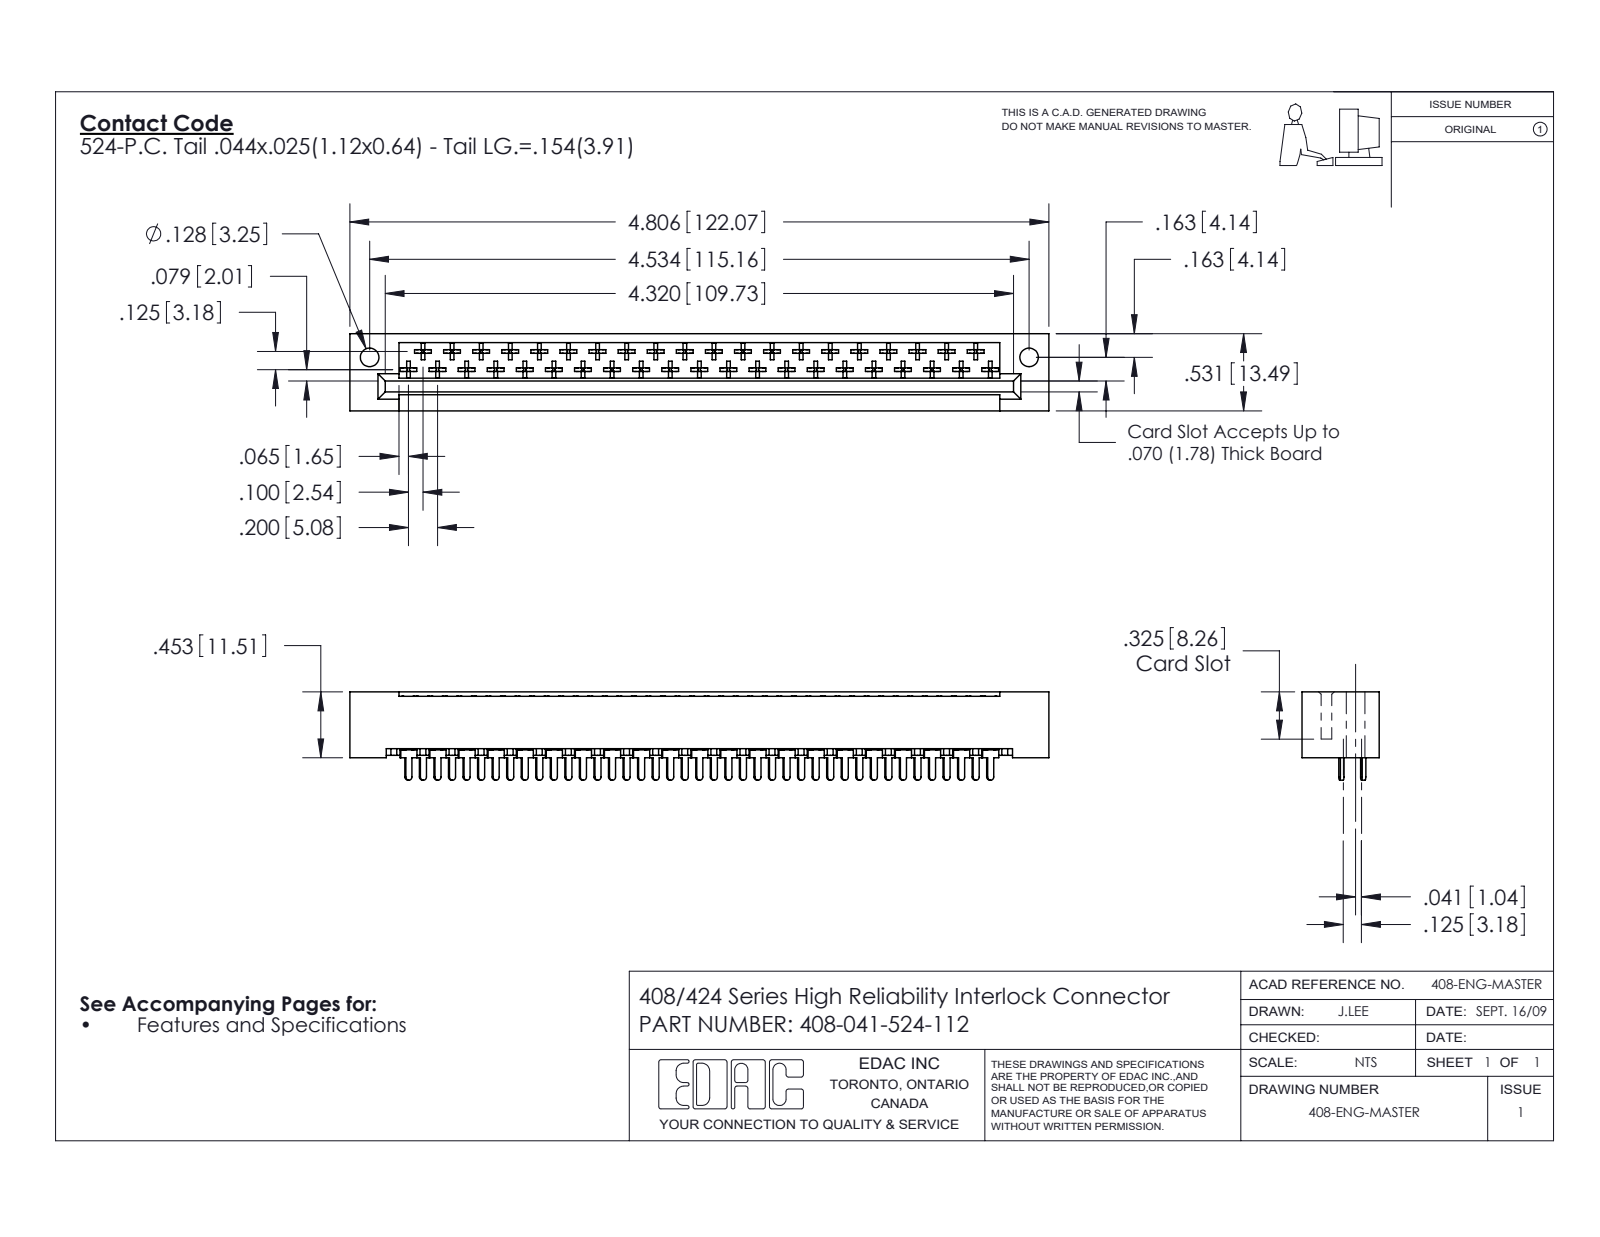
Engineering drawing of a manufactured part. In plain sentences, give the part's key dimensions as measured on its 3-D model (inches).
The part is named "408-041-524-112; 408 Part_041 - 1; 408-290-001_408-290-124 - Bottom; 408-290-001_408-290-124 - Top". Its 3-D file was written by "SolidWorks 2016 (CONFIG_CONTROL_DESIGN)". It is 42 solids with 2299 faces: 1758 planar, 377 cylindrical and 164 other. Overall it measures 4.806 by 0.607 by 0.531 inches. Its volume is 0.85 cubic inches and its surface area 25.92 square inches. Round holes: 2 of diameter 0.128. Partial cylindrical surfaces (rounded edges, fillets, slot ends): 246 of radius 0.01, 43 of radius 0.02, 41 of radius 0.022. The main face-to-face distances are 0.531, 0.125, 0.1, 0.025, 0.025, 0.4, 0.259, 0.272, 0.235, 0.296. The hole center spacings are 4.534.
